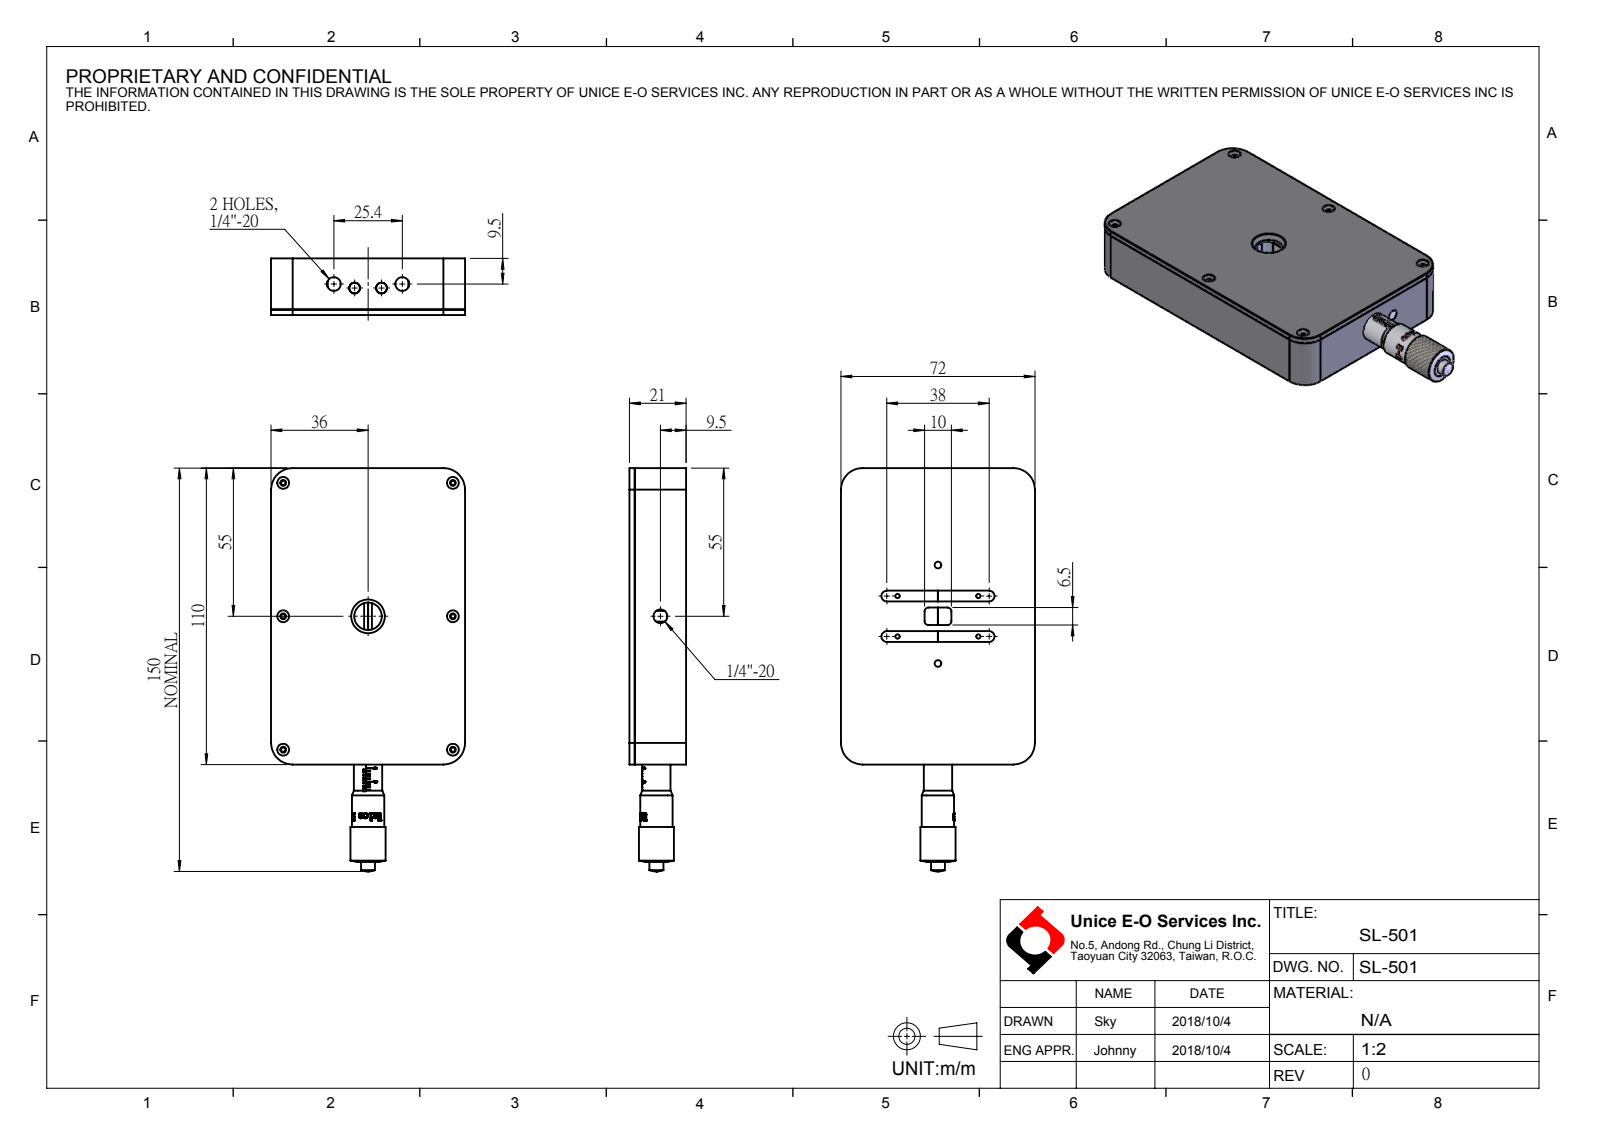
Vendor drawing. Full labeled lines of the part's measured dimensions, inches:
Part name (STEP PRODUCT): SL-501
STEP written by: SolidWorks 2016 (AUTOMOTIVE_DESIGN)
Units: inches
Bodies: 0 solids, 173 faces (65 planar, 76 cylindrical, 32 other)
Overall size (bounding box): 5.893 × 2.835 × 0.827
Round holes (diameter × count): ⌀0.063 ×6, ⌀0.087 ×6, ⌀0.201 ×3, ⌀0.098 ×2
Round bosses / shafts (diameter × count): ⌀0.512 ×1, ⌀0.472 ×1, ⌀0.413 ×1, ⌀0.205 ×1
Partial cylindrical surfaces — rounded edges, fillets, slot ends (radius × count): R0.059 ×4, R0.079 ×4, R0.118 ×4, R0.315 ×4, R0.235 ×1
Main face-to-face distances: 0.079, 0.748, 0.827, 0.591, 0.157, 2.835, 0.236, 0.433, 4.331, 0.669
Hole centre spacings: 1.949, 3.154, 2.48, 1.419, 1.448, 1.726, 1.768, 2.915
